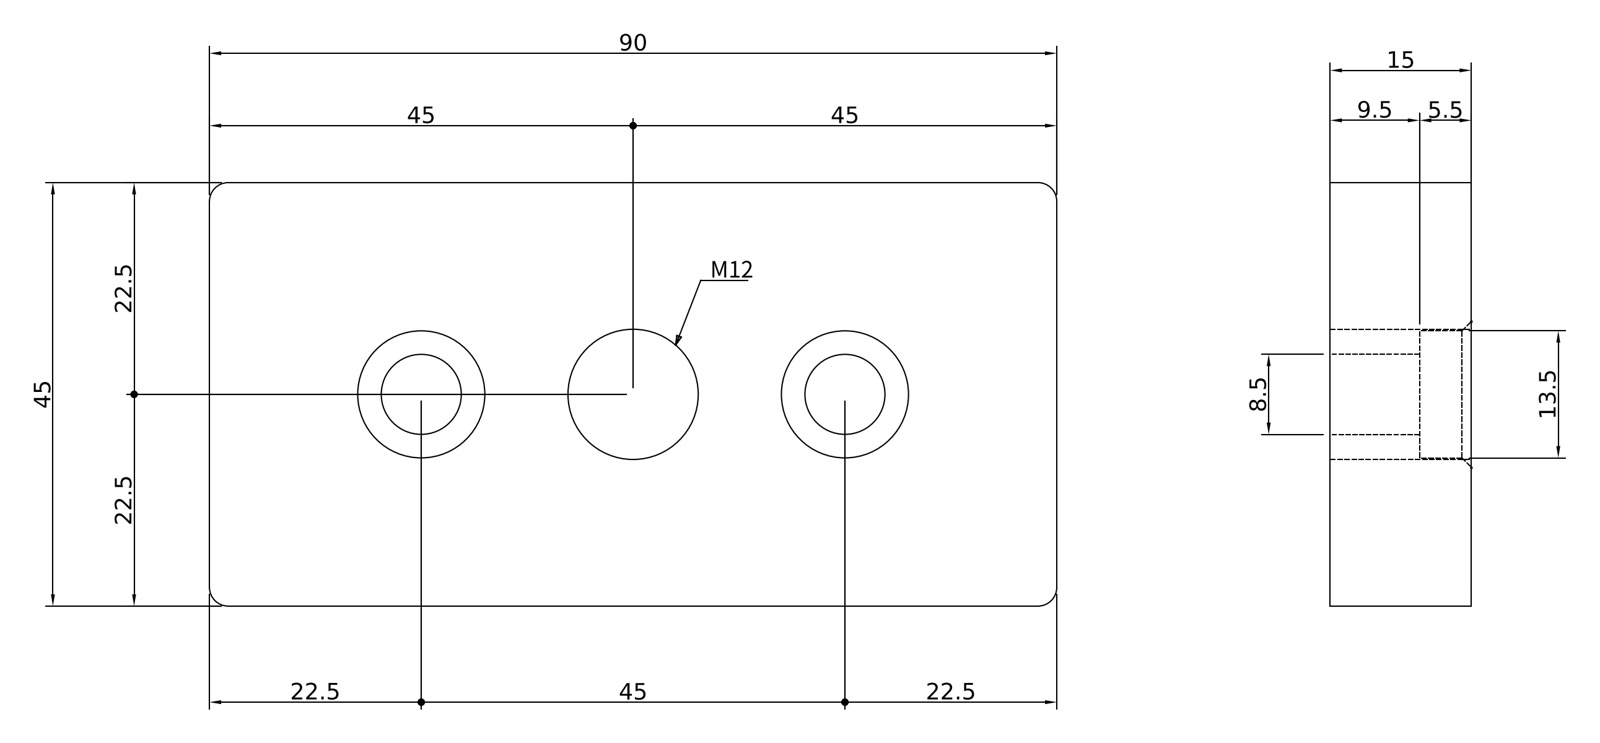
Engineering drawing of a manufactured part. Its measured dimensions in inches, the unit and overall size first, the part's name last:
Units: inches
Overall size (bounding box): 3.543 × 1.772 × 0.591
Round holes (diameter × count): ⌀0.335 ×2, ⌀0.531 ×2, ⌀0.545 ×1
Partial cylindrical surfaces — rounded edges, fillets, slot ends (radius × count): R0.079 ×4
Main face-to-face distances: 0.591, 1.772, 3.543, 0.374, 0.217
Hole centre spacings: 0.886, 1.772
Volume: 3.402 in³ · Surface area: 20.37 in²
Bodies: 1 solid, 19 faces (8 planar, 9 cylindrical, 2 other)
Part name (STEP PRODUCT): 440000003498
STEP written by: Autodesk Inventor 2016 (AUTOMOTIVE_DESIGN)
